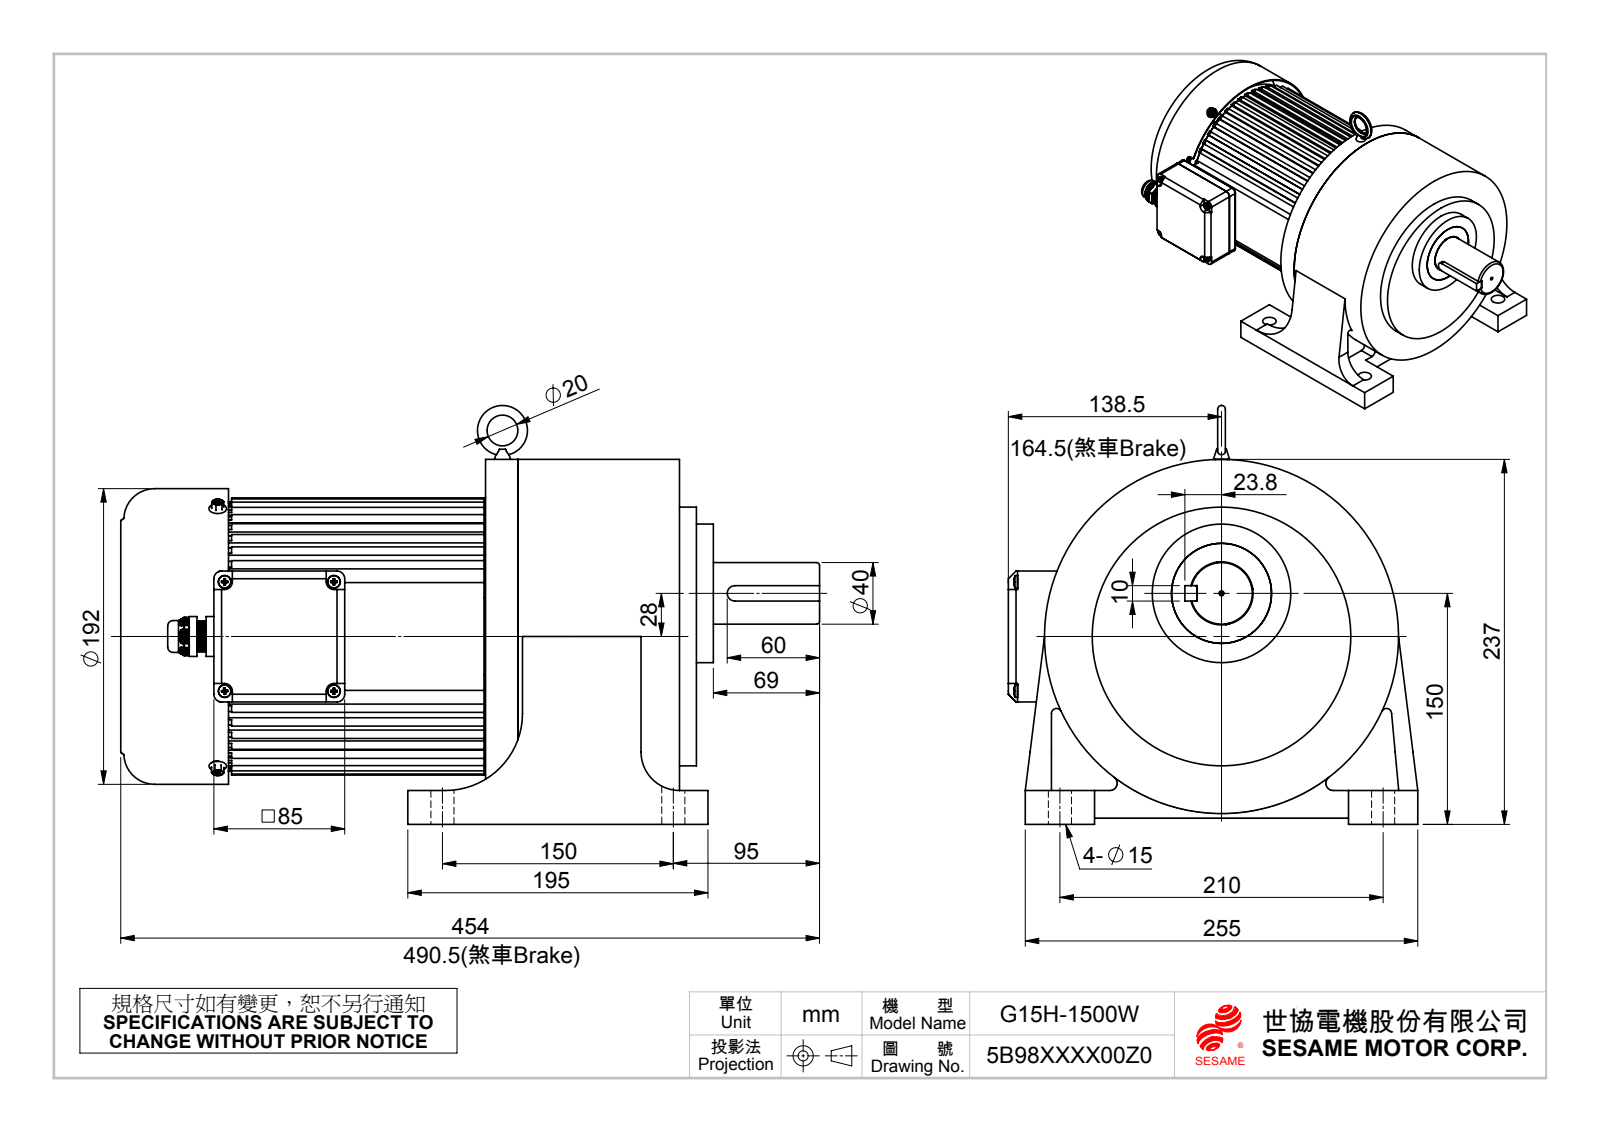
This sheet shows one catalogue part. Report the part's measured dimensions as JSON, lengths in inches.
{"part_name": "出線盒下蓋; 外六角內十字螺絲M5 x 10_ISO 4162 - M5 x 10 x 10-N; M8x16吊環(G14.G15前蓋用); 10x8xL_60L (+8 more)", "step_written_by": "SolidWorks 2010 (CONFIG_CONTROL_DESIGN)", "units": "inches", "bodies": {"solids": 20, "faces": 3126, "planar": 1195, "cylindrical": 867, "other": 1064}, "overall_size": [17.874, 10.709, 10.472], "volume_in3": 698.7, "surface_area_in2": 1265, "round_holes": [[0.197, 11], [0.13, 9], [0.236, 4], [0.315, 4], [0.591, 4], [0.165, 3], [0.079, 1], [0.256, 1], [0.268, 1], [0.425, 1], [0.65, 1], [0.787, 1]], "round_bosses_or_shafts": [[0.327, 4], [0.157, 4], [0.197, 3], [9.055, 1], [8.583, 1], [7.559, 1], [7.48, 1], [7.087, 1]], "partial_cylinders_radius": [[0.089, 42], [0.02, 24], [0.039, 24], [0.197, 10], [0.114, 6], [0.079, 4], [0.1, 4], [0.14, 4]], "face_to_face_distances": [0.197, 0.866, 1.063, 7.48, 7.677, 6.614, 0.039, 0.236, 9.291, 0.709], "hole_center_spacings": [1.772, 2.293, 2.795, 3.243, 0.433, 0.453, 0.575, 0.582]}
